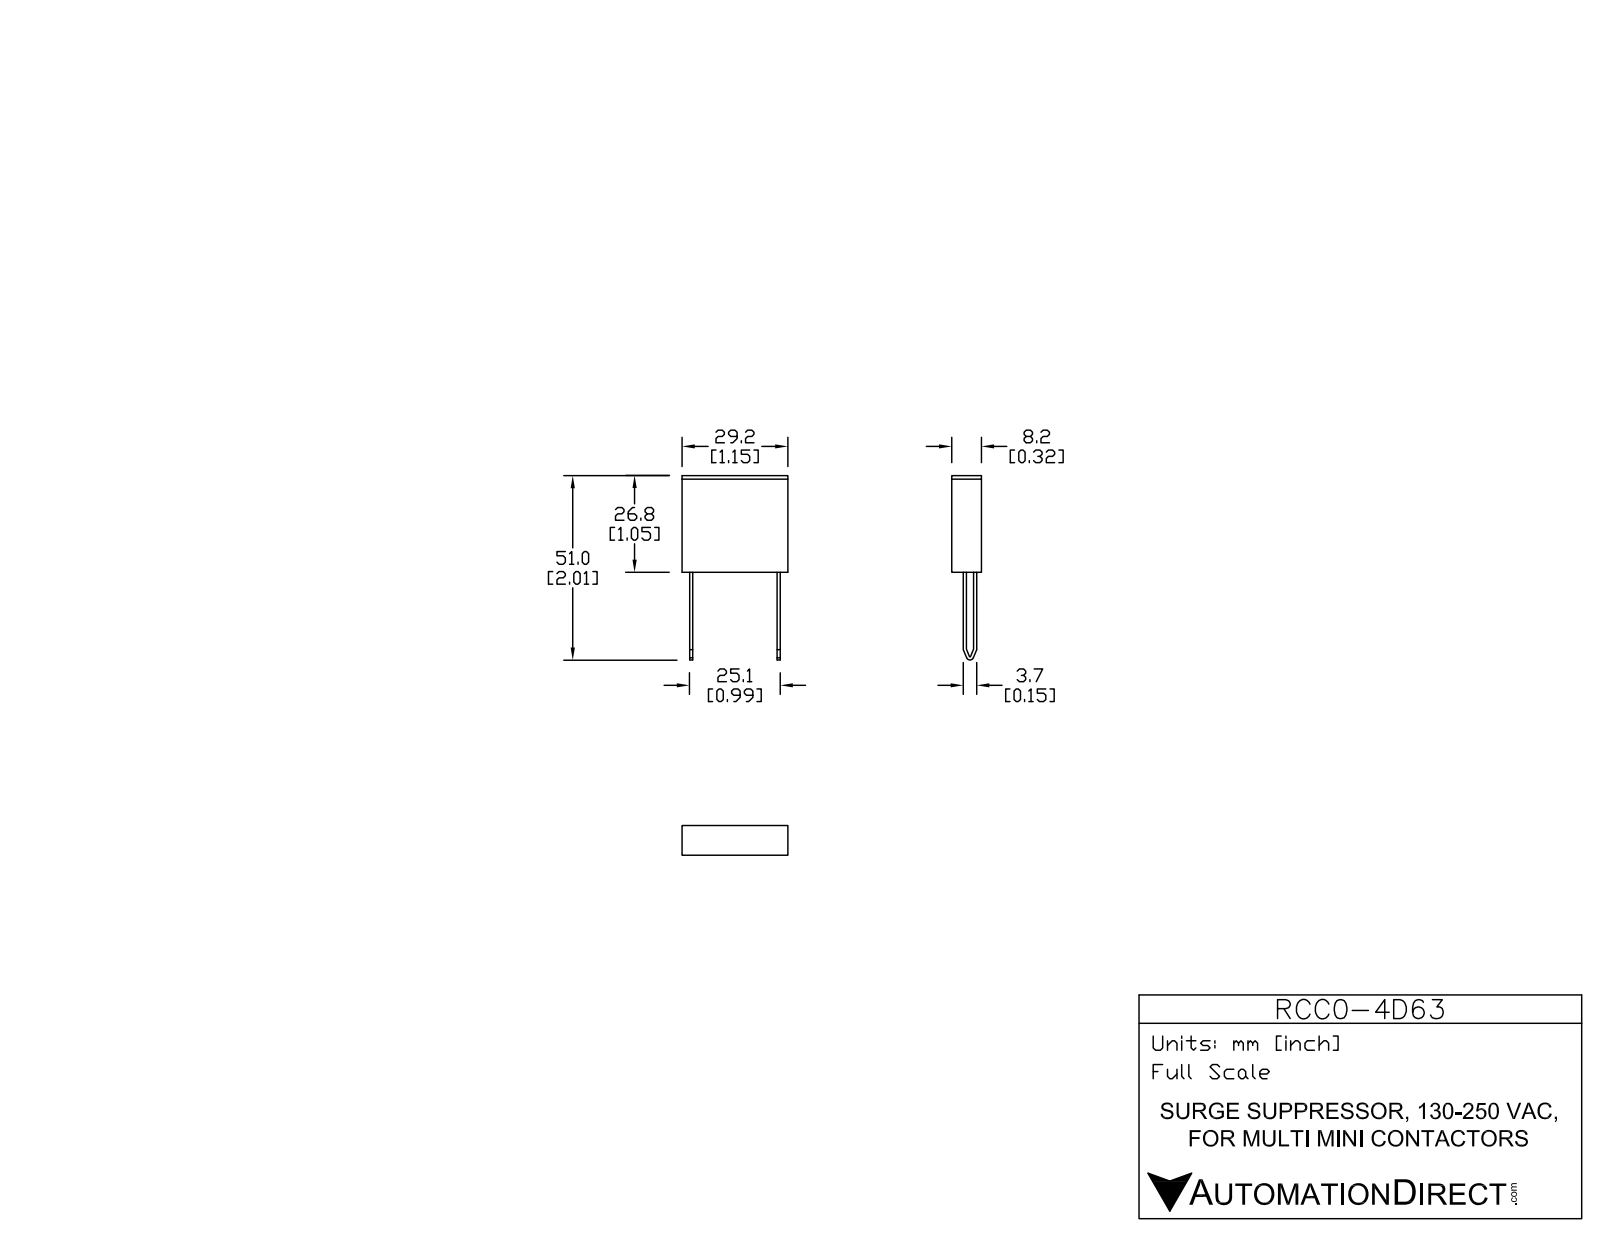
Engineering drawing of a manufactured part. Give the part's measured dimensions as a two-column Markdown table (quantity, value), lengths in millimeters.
| quantity | value |
| --- | --- |
| part name | RCC0-4D63 |
| STEP written by | SolidWorks 2013 (AUTOMOTIVE_DESIGN) |
| units | millimeters |
| bodies | 1 solid, 34 faces (26 planar, 8 cylindrical, 0 other) |
| overall size | 50.9 × 29.2 × 8.2 |
| volume | 6 463 mm³ |
| surface area | 2 803 mm² |
| partial cylindrical surfaces (radius × count) | 0.15 × 1, 1 × 1 |
| main face-to-face distances | 8.2, 26.7, 29.2, 0.85, 2.1, 27.1, 2.95, 26.25, 24.15, 2.85 |
